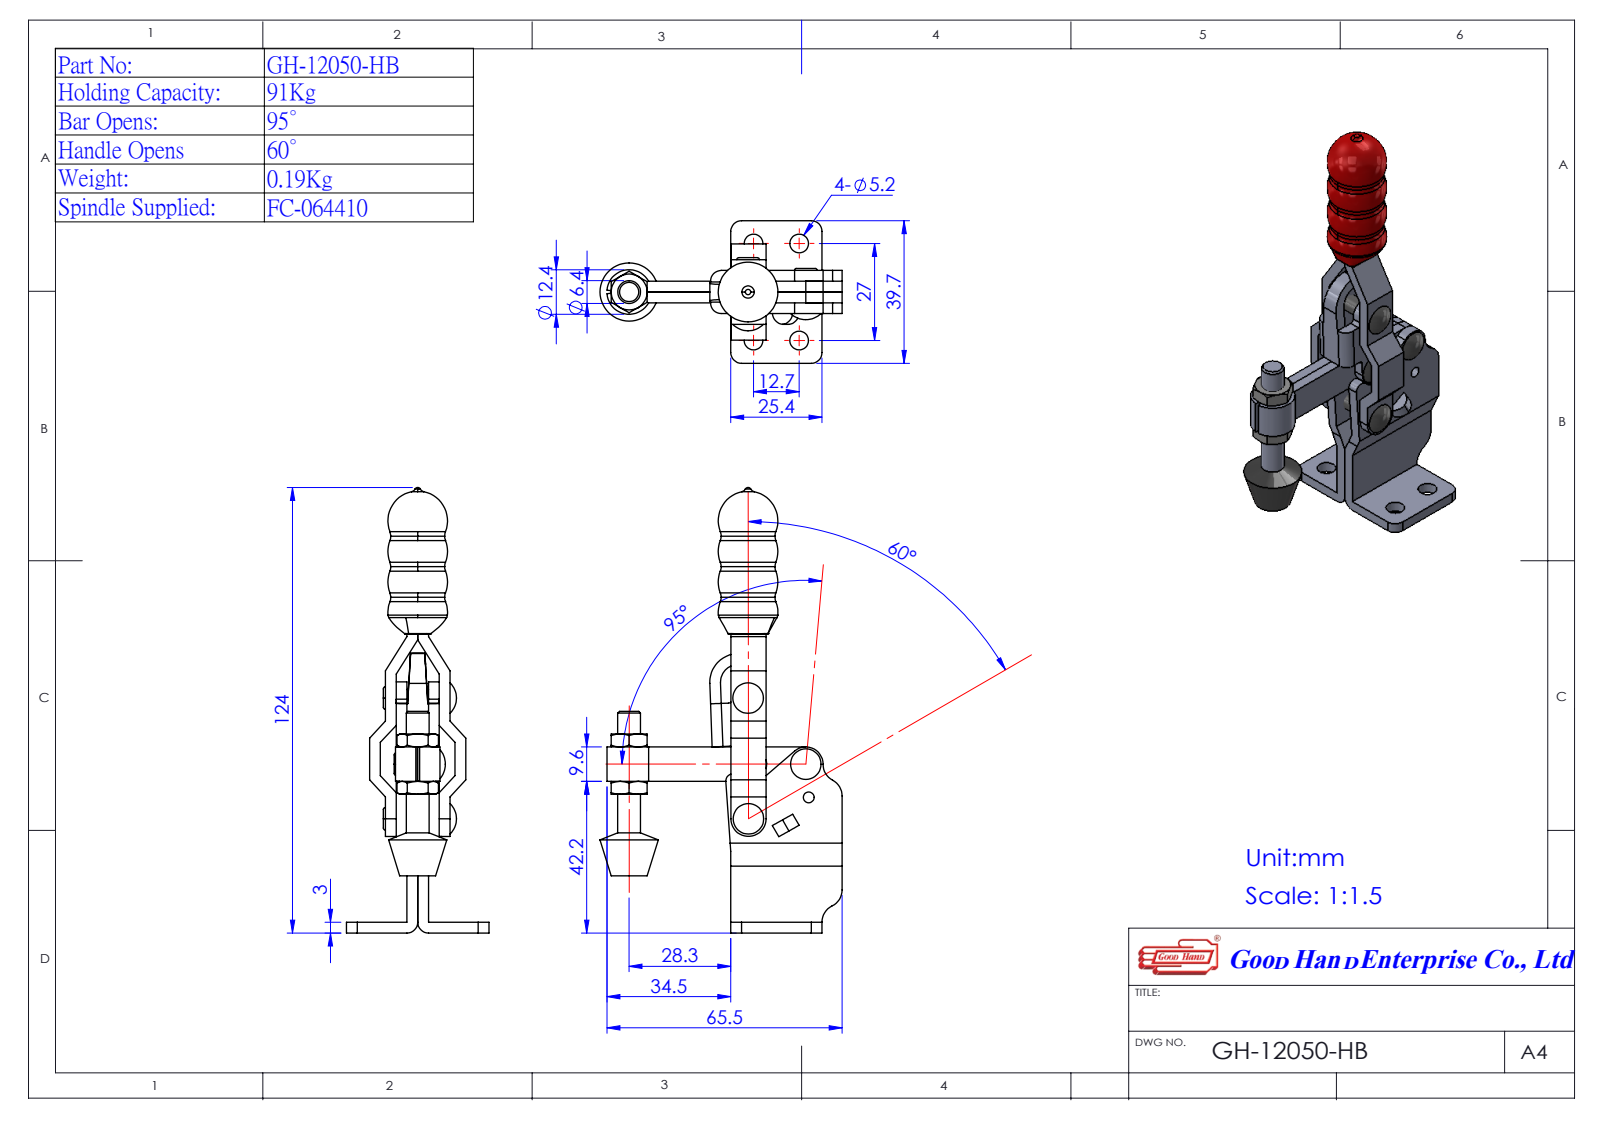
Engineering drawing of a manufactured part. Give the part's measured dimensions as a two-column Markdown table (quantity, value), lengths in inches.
| quantity | value |
| --- | --- |
| part name | 11205008-1^GH-12050-HB(簡化)-1; Group5^GH-12050-HB(簡化)-1; Group3^GH-12050-HB(簡化)-1; GH-12050-HB(簡化)-1 (+2 more) |
| STEP written by | SolidWorks 2016 (AUTOMOTIVE_DESIGN) |
| units | inches |
| bodies | 5 solids, 264 faces (108 planar, 96 cylindrical, 60 other) |
| overall size | 4.87 × 2.672 × 1.563 |
| volume | 1.897 in³ |
| surface area | 29.99 in² |
| round holes (diameter × count) | 0.118 × 5, 0.205 × 4, 0.252 × 1 |
| round bosses / shafts (diameter × count) | 0.197 × 3, 0.488 × 1, 0.25 × 1 |
| partial cylindrical surfaces (radius × count) | 0.197 × 6, 0.118 × 4, 0.079 × 3, 0.039 × 2, 0.138 × 2, 0.177 × 2, 0.189 × 1, 0.193 × 1 |
| main face-to-face distances | 0.118, 0.354, 0.236, 0.472, 0.173, 0.291, 0.646, 0.764, 0.591, 0.378 |
| hole center spacings | 0.5, 1.063, 1.175, 0.365, 0.599, 0.614, 0.701, 0.724 |
